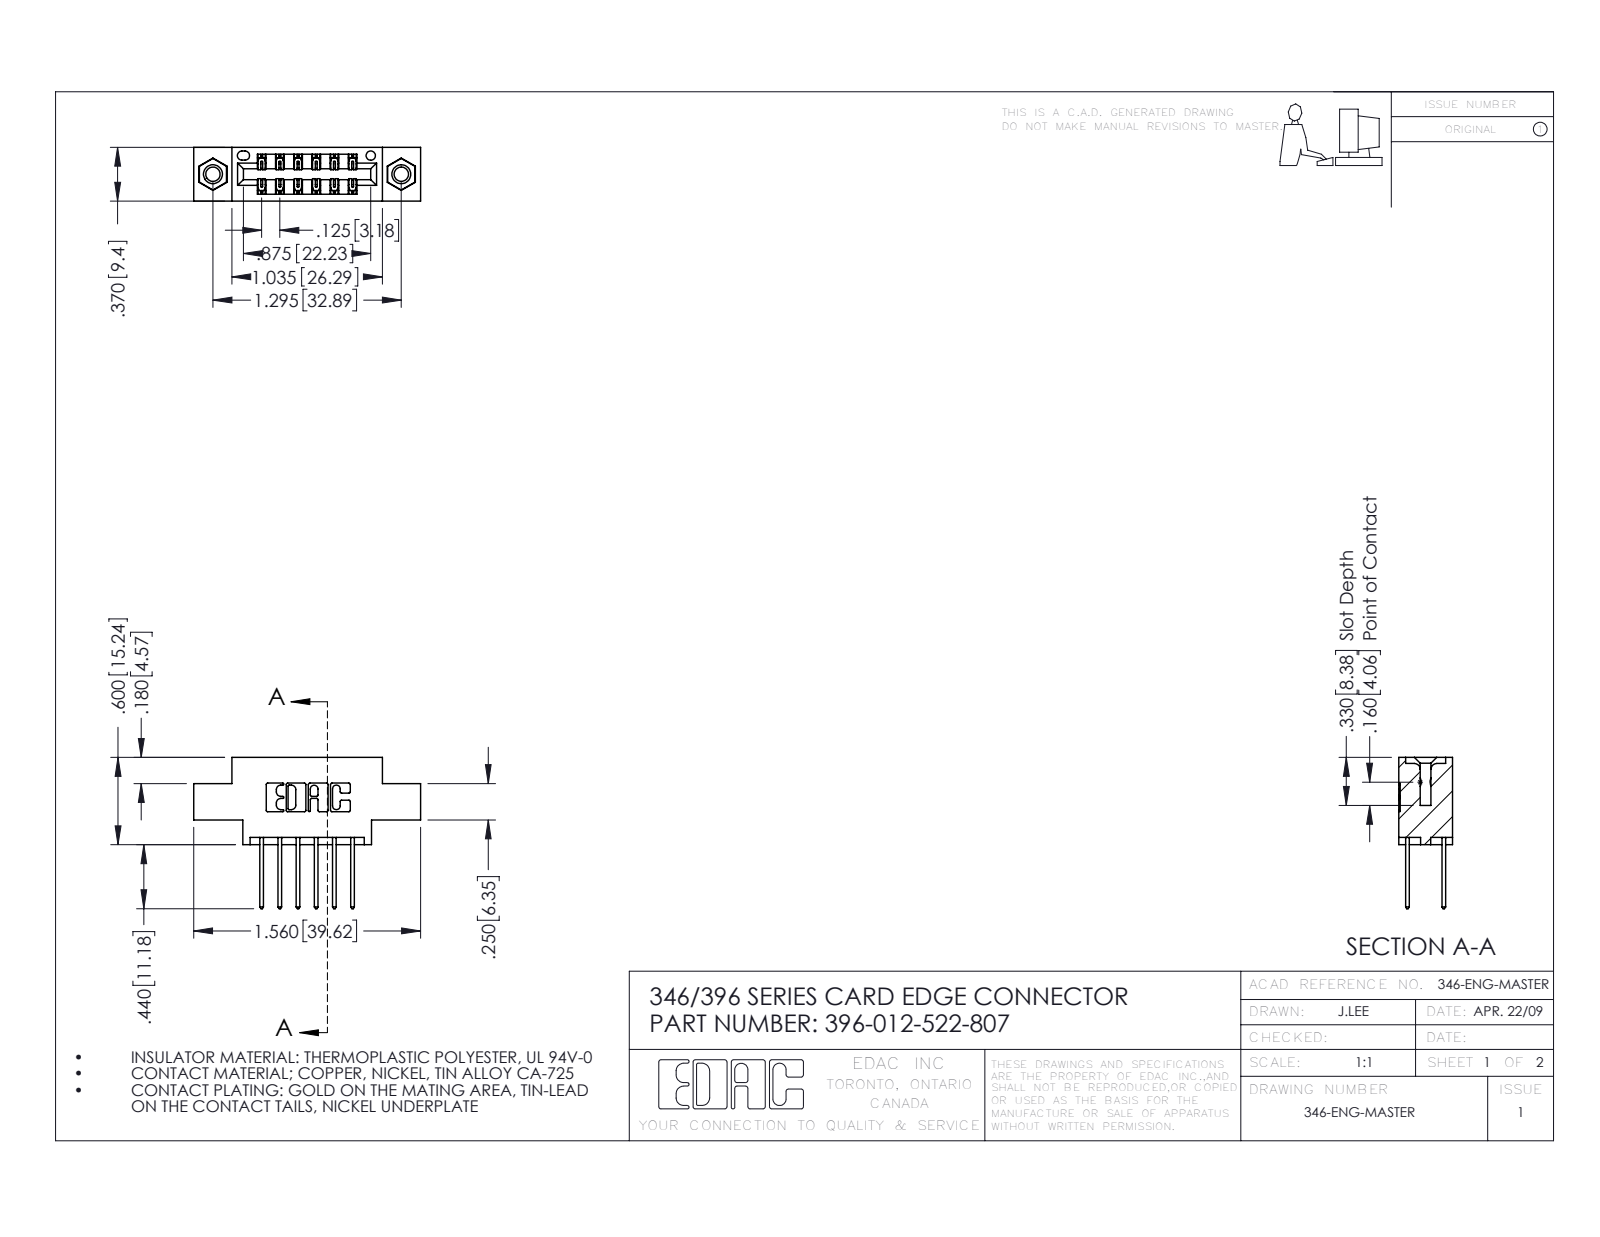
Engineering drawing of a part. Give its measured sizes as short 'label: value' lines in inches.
name: 396-012-522-807; 345-292-001_345-293-122; 345-250-001_345-250-005-103; 346 Part_0.170 Offset - 0.156 Dia-TI
written by: SolidWorks 2016 (CONFIG_CONTROL_DESIGN)
unit: in
bodies: 15 solids, 810 faces (532 planar, 262 cylindrical, 16 other)
size: 1.56 × 1.04 × 0.37
volume: 0.21 in³; area: 7.018 in²
holes: 2× ⌀0.098, 2× ⌀0.125, 2× ⌀0.156, 1× ⌀0.064
bosses: 2× ⌀0.155
rounds: 22× R0.01, 18× R0.006, 12× R0.01, 6× R0.007, 6× R0.031, 3× R0.026, 2× R0.014, 2× R0.022
face distances: 0.25, 0.37, 0.048, 0.322, 0.072, 0.298, 0.025, 0.222, 0.275, 0.148
hole spacings: 0.246, 1.092, 1.295
